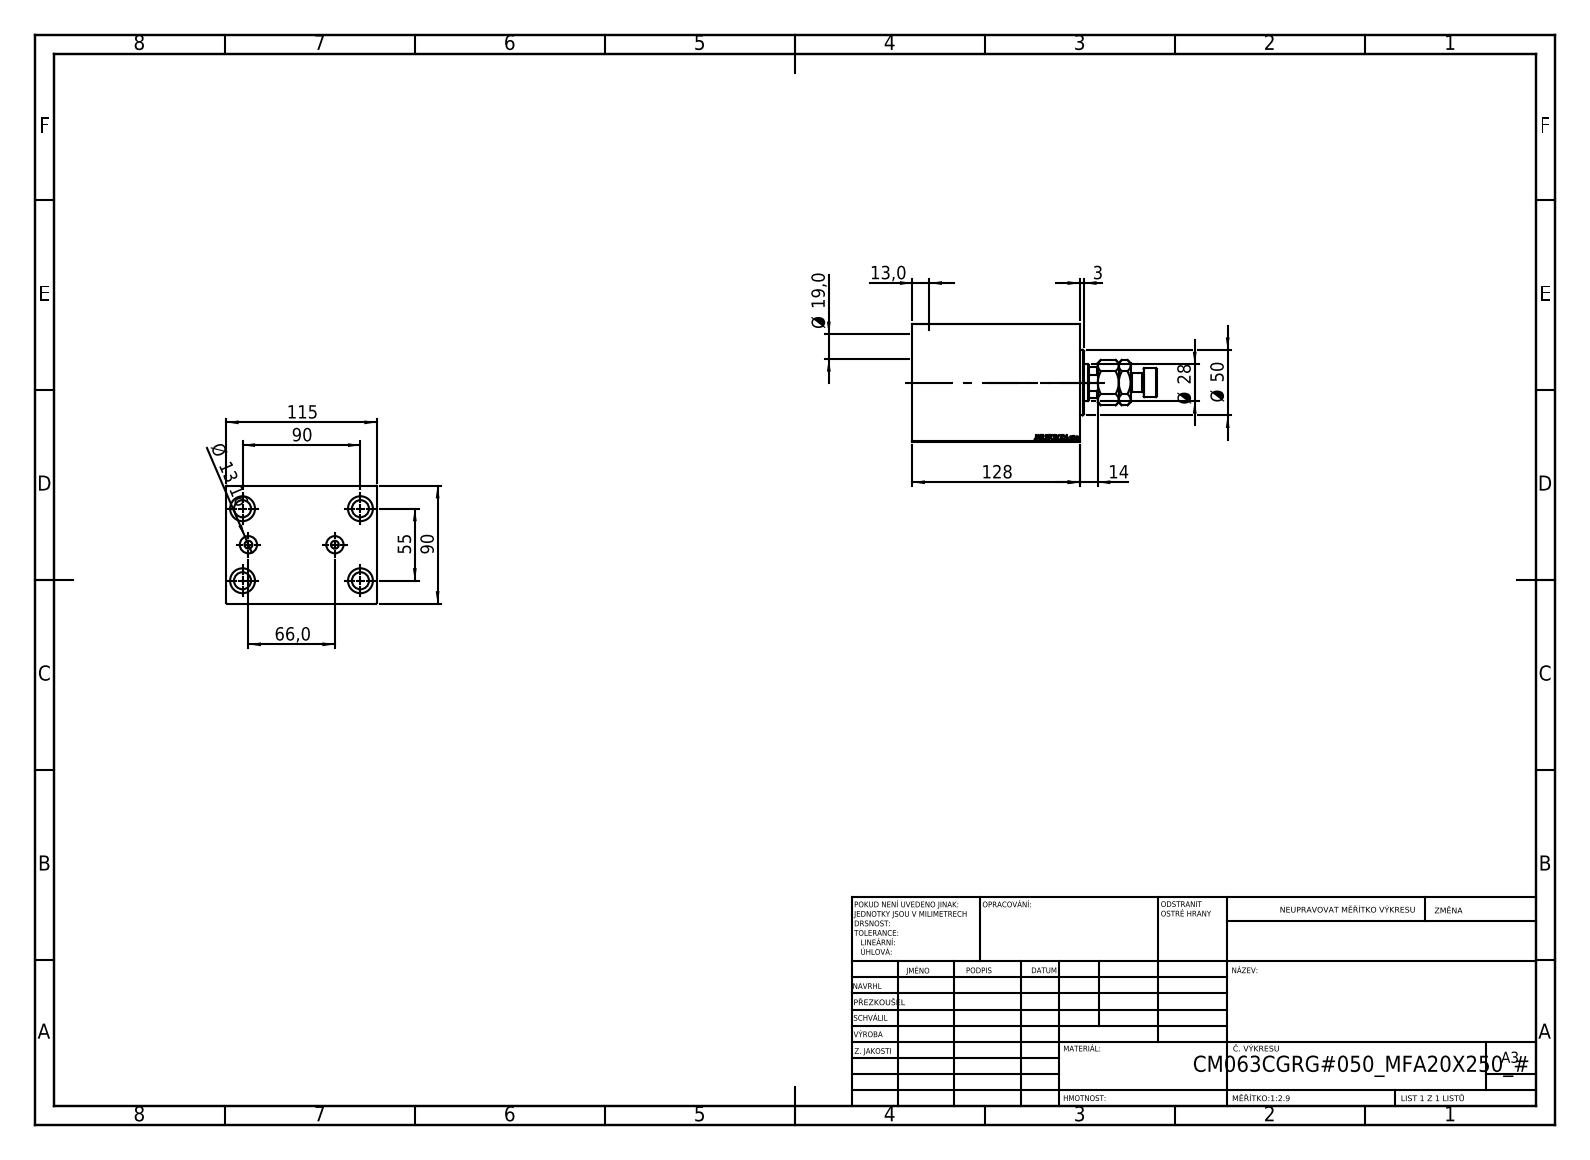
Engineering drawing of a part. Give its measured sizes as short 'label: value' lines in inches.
name: V450CM_VC_B; V450CM_C_Body; MFA; V450CM_C_VCP
written by: SolidWorks 2019 (CONFIG_CONTROL_DESIGN)
unit: in
bodies: 4 solids, 912 faces (424 planar, 62 cylindrical, 426 other)
size: 7.343 × 4.528 × 3.543
volume: 69.51 in³; area: 249.4 in²
holes: 4× ⌀0.512, 4× ⌀0.748, 2× ⌀0.236, 2× ⌀0.518, 1× ⌀0.728, 1× ⌀1.102, 1× ⌀1.24, 1× ⌀2.48, 1× ⌀2.559, 1× ⌀2.835
bosses: 1× ⌀1.969, 1× ⌀0.866, 1× ⌀0.551
rounds: 1× R0.531
face distances: 3.543, 4.528, 5.039, 0.689, 4.35, 0.531, 3.819, 4.508, 2.5, 1.85
hole spacings: 2.076, 1.097, 1.327, 2.165, 2.979, 3.536, 3.543, 4.153
